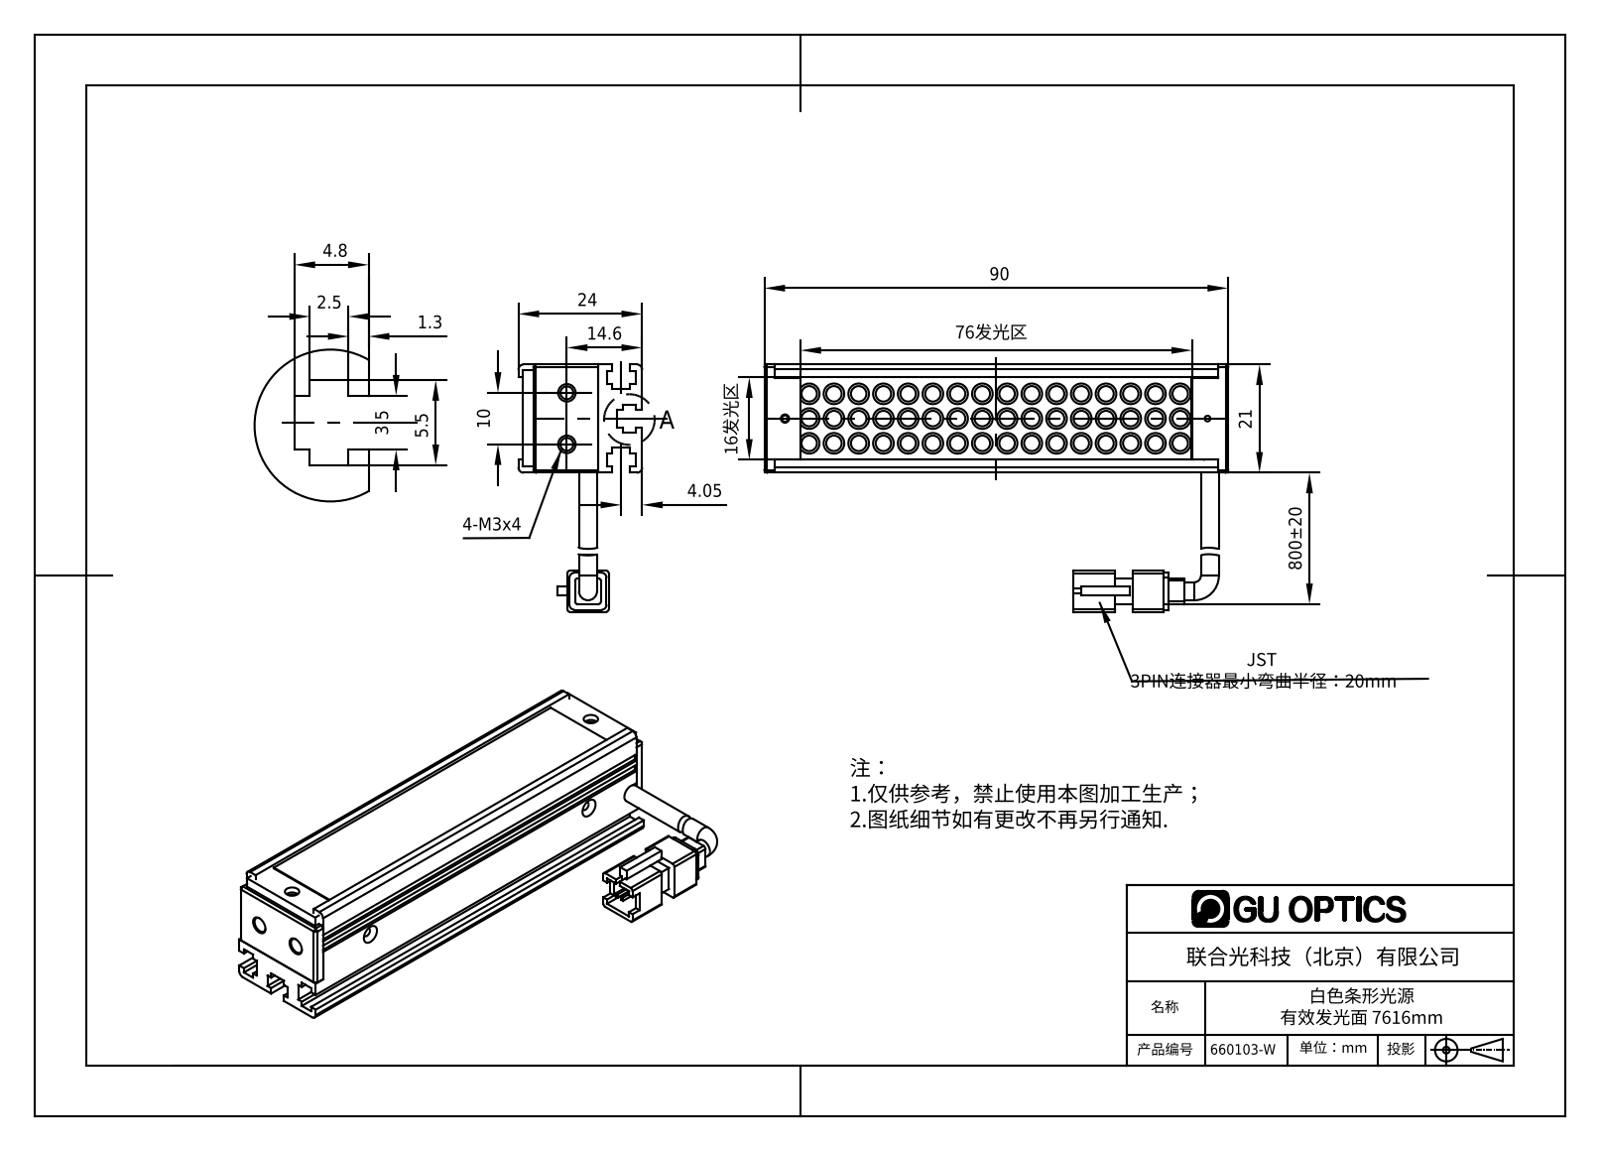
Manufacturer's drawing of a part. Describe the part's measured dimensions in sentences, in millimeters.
The part is named "660103-W". Its 3-D file was written by "SolidWorks 2016 (AUTOMOTIVE_DESIGN)". It is 8 solids with 728 faces: 302 planar, 275 cylindrical and 151 other. Overall it measures 90 by 48 by 24 millimeters. Its volume is 27 365 cubic millimeters and its surface area 30 230 square millimeters. Round holes: 5 of diameter 1.6, 2 of diameter 1.5, 2 of diameter 1.7, 2 of diameter 2.5, 2 of diameter 2.8, 2 of diameter 3, 1 of diameter 1.1, 1 of diameter 1.25, 1 of diameter 2. Round bosses or shafts: 48 of diameter 4, 48 of diameter 3, 2 of diameter 3.5. Partial cylindrical surfaces (rounded edges, fillets, slot ends): 12 of radius 1, 8 of radius 0.5, 1 of radius 1.65. The main face-to-face distances are 1, 2, 2.5, 18.5, 14.6, 21, 1.3, 3.5, 8.5, 12.6. The hole center spacings are 82, 7, 11.12, 12.25, 71.02, 71.21, 82.3, 10.
